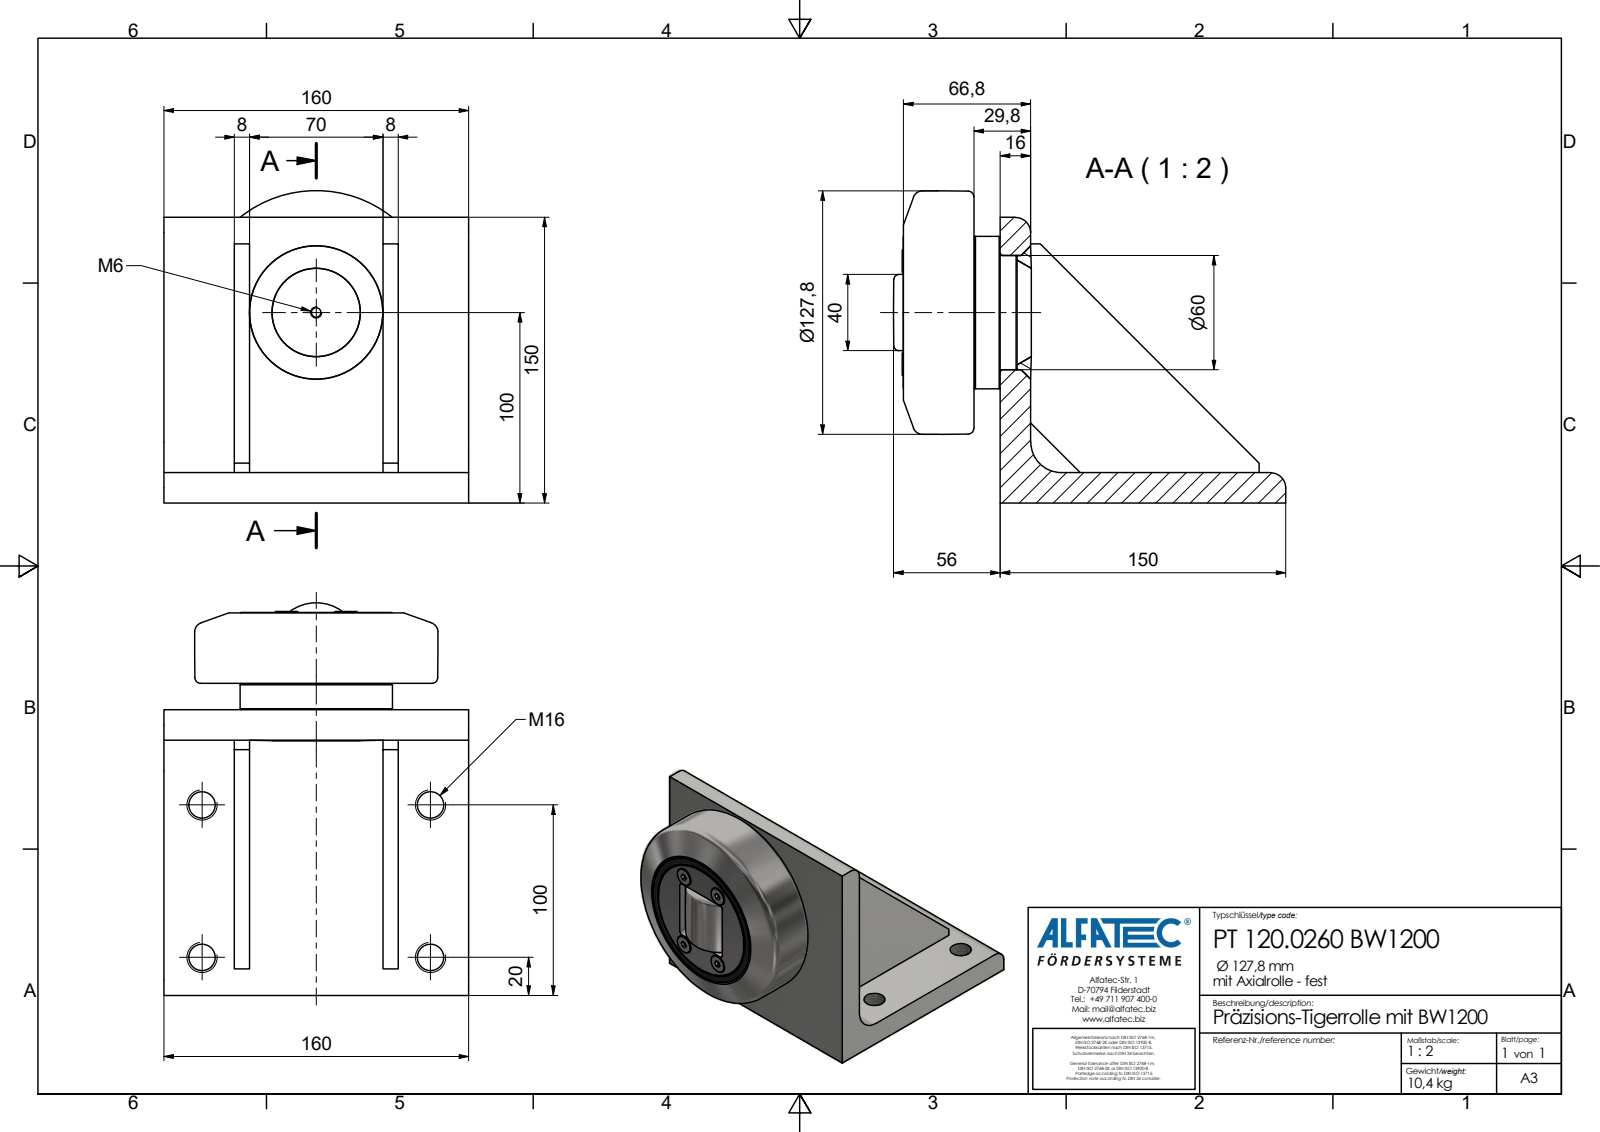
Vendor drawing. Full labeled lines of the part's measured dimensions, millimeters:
Part name (STEP PRODUCT): PT 120.0260 BW1200_Kontur
STEP written by: Autodesk Inventor 2020 (AP242_MANAGED_MODEL_BASED_3D_ENGINEERING_MIM_LF)
Units: millimetres
Bodies: 1 solid, 93 faces (64 planar, 14 cylindrical, 15 other)
Overall size (bounding box): 205.99 × 163.9 × 160
Volume: 1 367 000 mm³ · Surface area: 166 172 mm²
Round holes (diameter × count): ⌀13.84 ×4, ⌀4.92 ×1
Round bosses / shafts (diameter × count): ⌀11.7 ×4, ⌀80 ×1
Partial cylindrical surfaces — rounded edges, fillets, slot ends (radius × count): R8 ×2, R16 ×1
Main face-to-face distances: 16, 8, 78, 37, 45, 115, 123, 70, 86, 29.8
Hole centre spacings: 80, 120, 144.22
